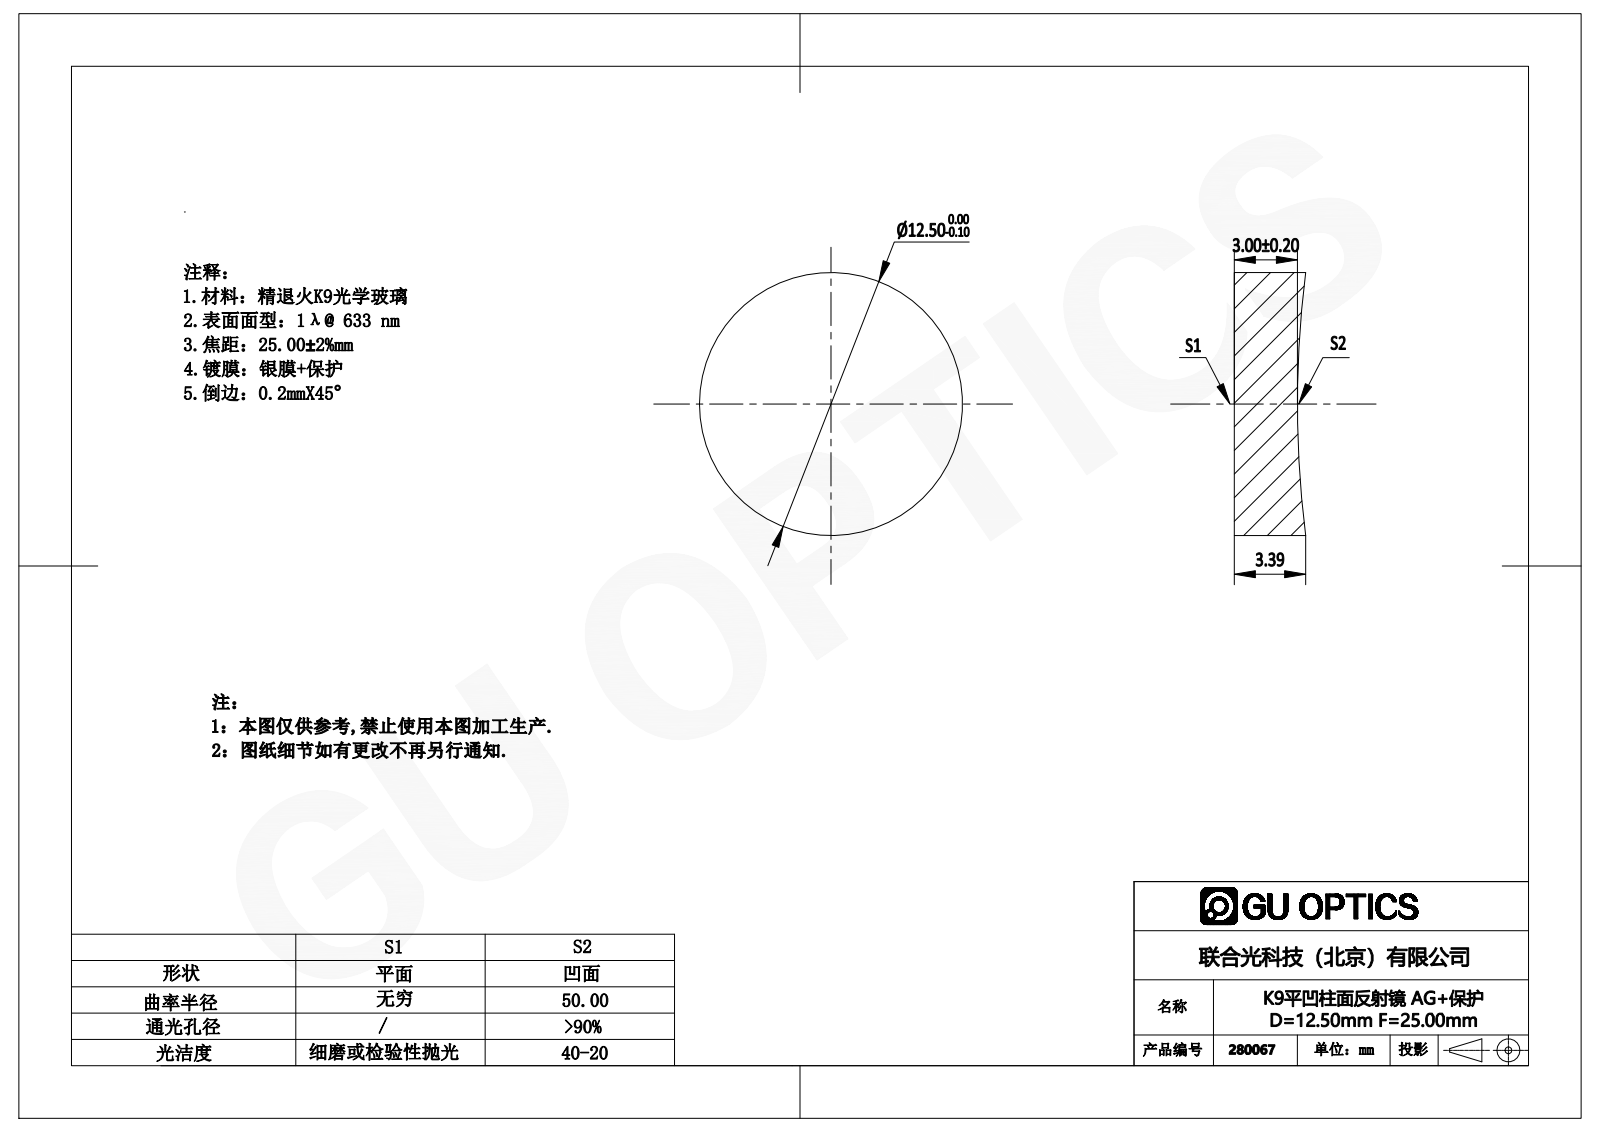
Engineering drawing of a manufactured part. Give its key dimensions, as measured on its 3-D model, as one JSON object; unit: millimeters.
{"part_name": "280001", "step_written_by": "SolidWorks 2020 (CONFIG_CONTROL_DESIGN)", "units": "millimeters", "bodies": {"solids": 1, "faces": 3, "planar": 1, "cylindrical": 2, "other": 0}, "overall_size": [12.5, 12.5, 3.39], "volume_mm3": 380, "surface_area_mm2": 371, "round_bosses_or_shafts": [[12.5, 1]], "partial_cylinders_radius": [[50, 1]]}
